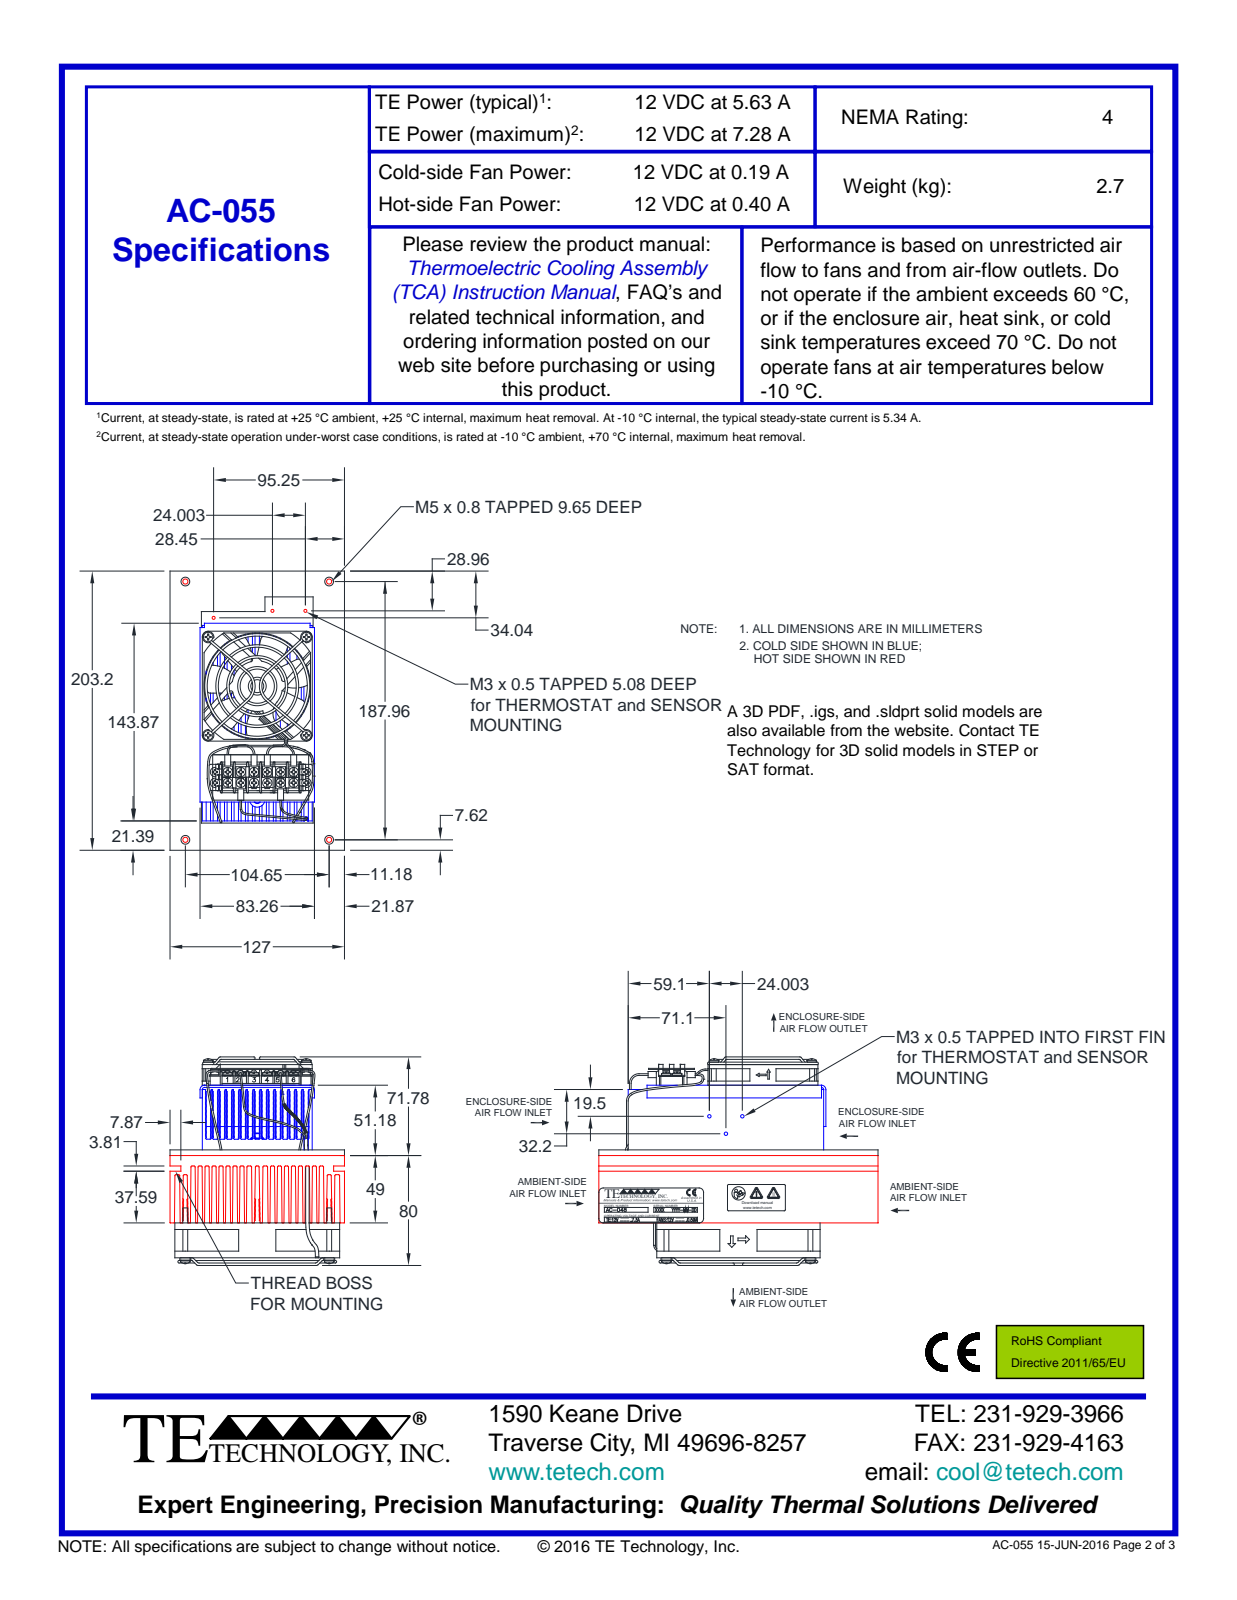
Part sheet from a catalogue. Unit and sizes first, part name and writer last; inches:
Units: inches
Overall size (bounding box): 8 × 5.951 × 5.01
Round holes (diameter × count): ⌀0.104 ×15, ⌀0.177 ×8, ⌀0.166 ×7, ⌀0.25 ×7, ⌀0.075 ×6, ⌀0.139 ×6, ⌀0.155 ×6, ⌀0.097 ×5, ⌀0.085 ×4, ⌀0.163 ×4, ⌀0.17 ×4, ⌀0.177 ×4
Round bosses / shafts (diameter × count): ⌀0.056 ×29, ⌀0.071 ×20, ⌀0.138 ×19, ⌀0.27 ×16, ⌀0.06 ×15, ⌀0.322 ×8, ⌀0.164 ×8, ⌀0.193 ×6
Partial cylindrical surfaces — rounded edges, fillets, slot ends (radius × count): R0.03 ×54, R0.01 ×52, R0.039 ×49, R0.031 ×24, R0.038 ×21, R0.031 ×12, R0.032 ×12, R0.079 ×11
Main face-to-face distances: 0.2, 0.4, 0.6, 0.8, 1, 2.075, 2.275, 1.875, 1.675, 2.475
Hole centre spacings: 0.75, 0.375, 0.31, 0.811, 0.375, 0.486, 1.125, 1.5
Volume: 70.26 in³ · Surface area: 1 355 in²
Bodies: 144 solids, 3701 faces (2025 planar, 787 cylindrical, 889 other)
Part name (STEP PRODUCT): cold sink ac-055; cold-sink shroud AC-055; module gasket ac-055; outer-gasket AC-055 (+8 more)
STEP written by: Alibre (AUTOMOTIVE_DESIGN)
